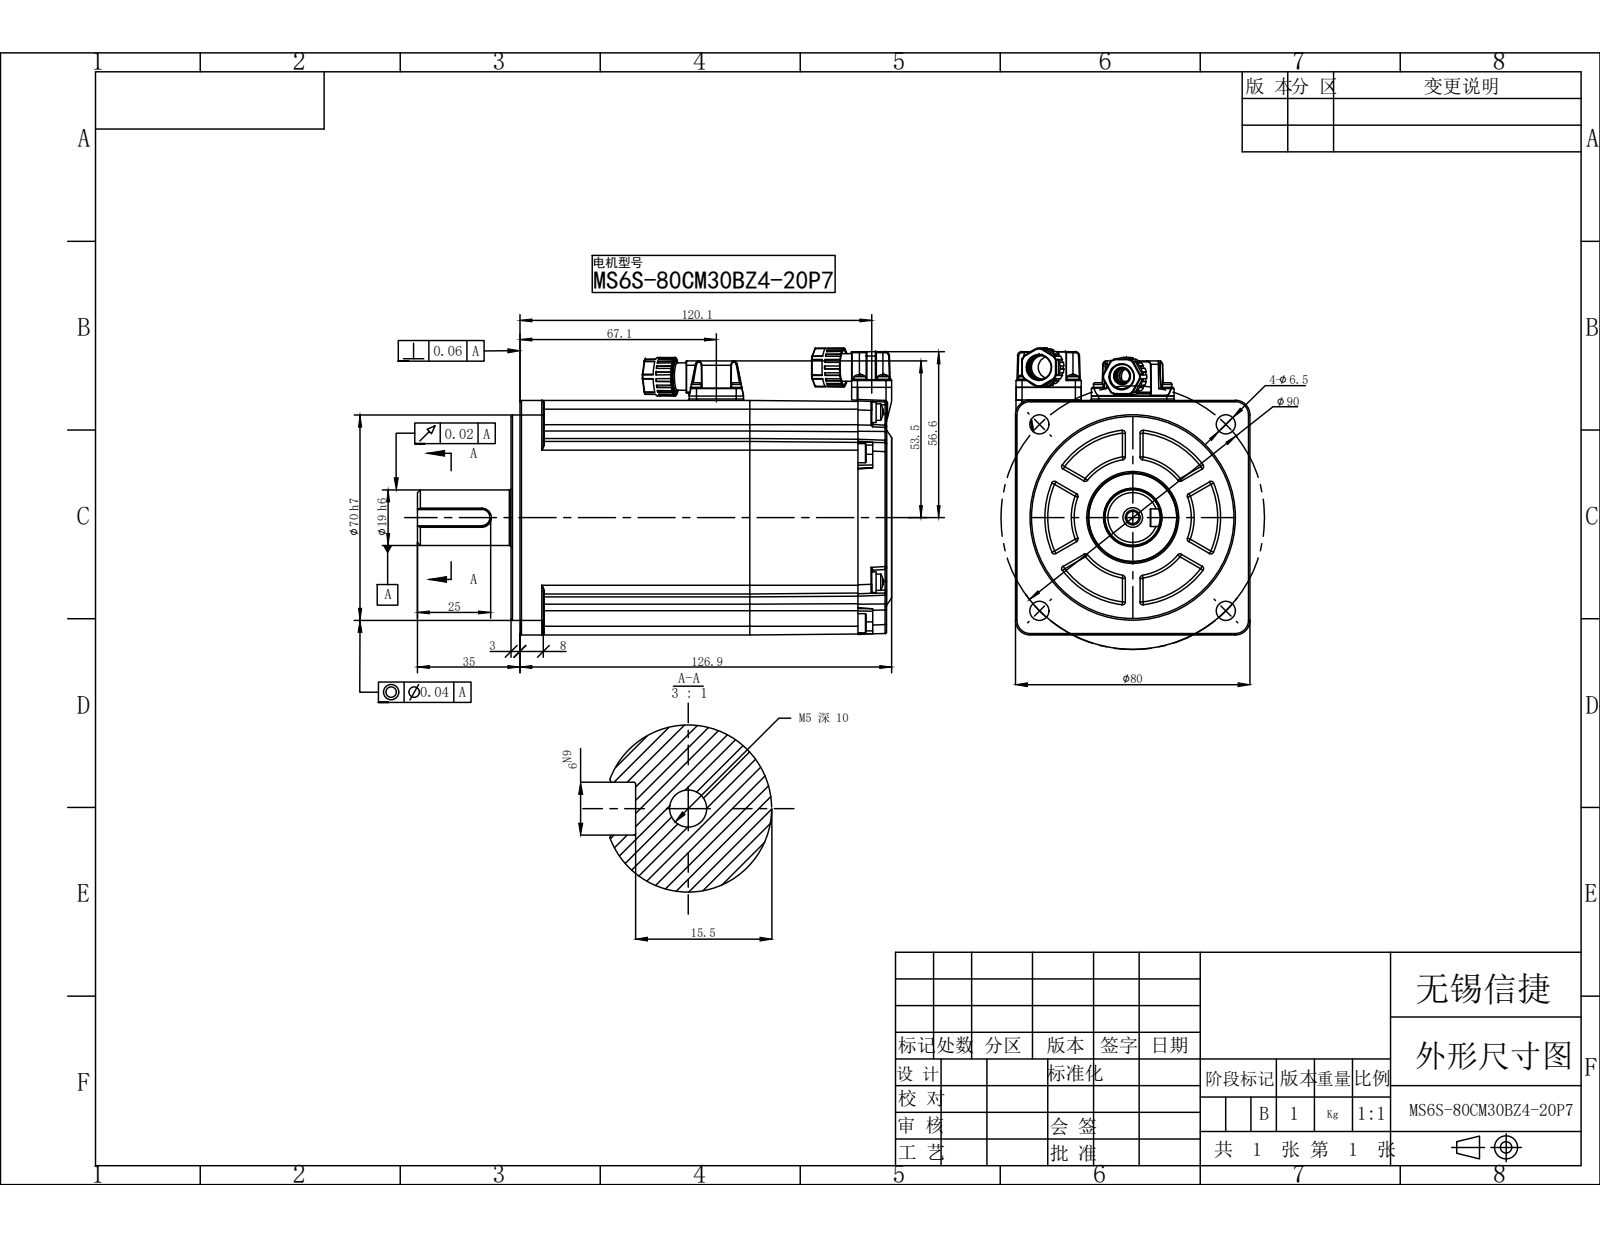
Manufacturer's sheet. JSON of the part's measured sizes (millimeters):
{"part_name": "MS6S-80CM30BZ4-20P7", "step_written_by": "SolidWorks 2022 (CONFIG_CONTROL_DESIGN)", "units": "millimeters", "bodies": {"solids": 0, "faces": 1361, "planar": 490, "cylindrical": 479, "other": 392}, "overall_size": [161.9, 97.86, 80], "round_holes": [[6.5, 4], [11.7, 2], [4.2, 1], [5, 1], [5.5, 1], [10.4, 1], [11.5, 1], [20, 1], [30, 1]], "round_bosses_or_shafts": [[7, 4], [6.53, 4], [5.6, 4], [4, 4], [3.9, 4], [3.3, 4], [9.4, 2], [70, 1]], "partial_cylinders_radius": [[0.5, 50], [0.3, 40], [1, 39], [3, 29], [0.2, 21], [0.35, 20], [1.5, 13], [0.15, 8]], "face_to_face_distances": [80, 14, 66, 126.9, 1.8, 125.1, 115.4, 11.5, 9.7, 3], "hole_center_spacings": [45, 63.64, 40.06, 90, 40.13, 40.14]}
